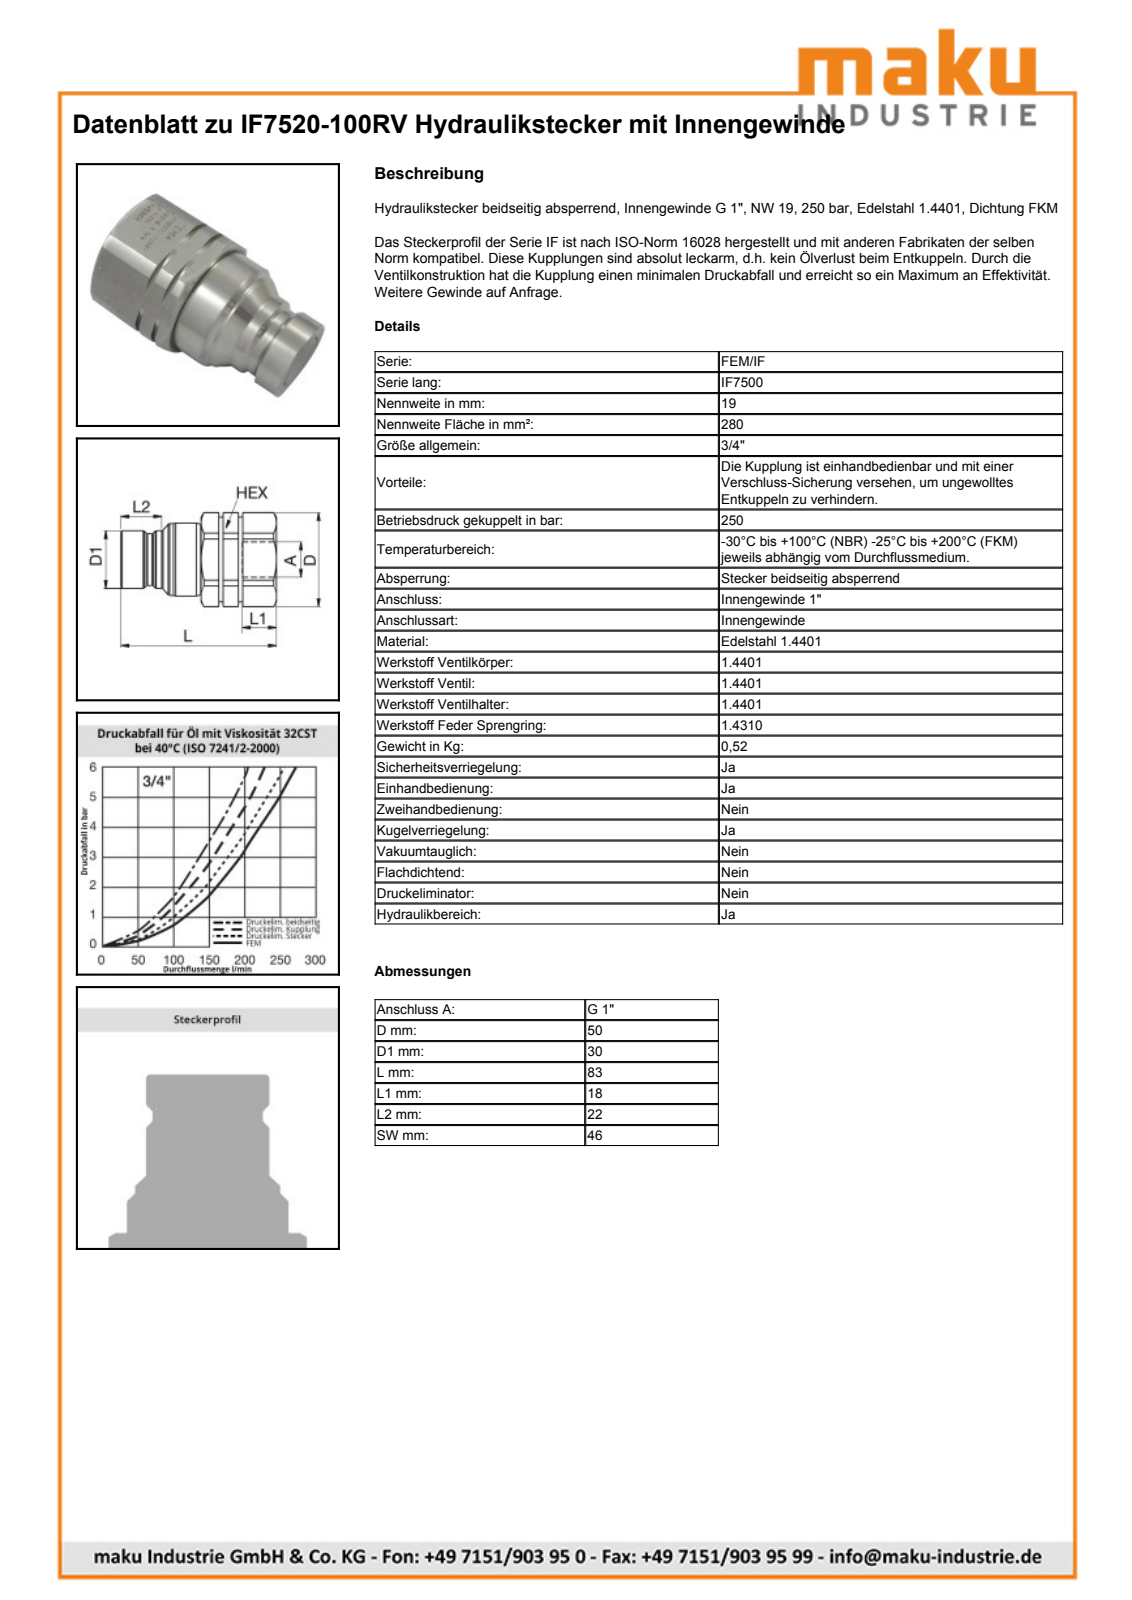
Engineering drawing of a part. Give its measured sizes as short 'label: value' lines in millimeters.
name: IF7520-100RV
written by: SolidWorks 2009 (AUTOMOTIVE_DESIGN)
unit: mm
bodies: 1 solid, 147 faces (37 planar, 54 cylindrical, 56 other)
size: 82.6 × 50 × 46
volume: 91 353 mm³; area: 18 119 mm²
holes: 1× ⌀20.7, 1× ⌀23.5, 1× ⌀30.29, 1× ⌀40.38, 1× ⌀42.2
bosses: 1× ⌀42, 1× ⌀38.05, 1× ⌀37.8, 1× ⌀29.95, 1× ⌀26.9
rounds: 1× R23.5, 1× R25
face distances: 46, 25.16, 57.36, 82.52, 57.44, 82.6, 41.6, 41.52, 15.84, 41
